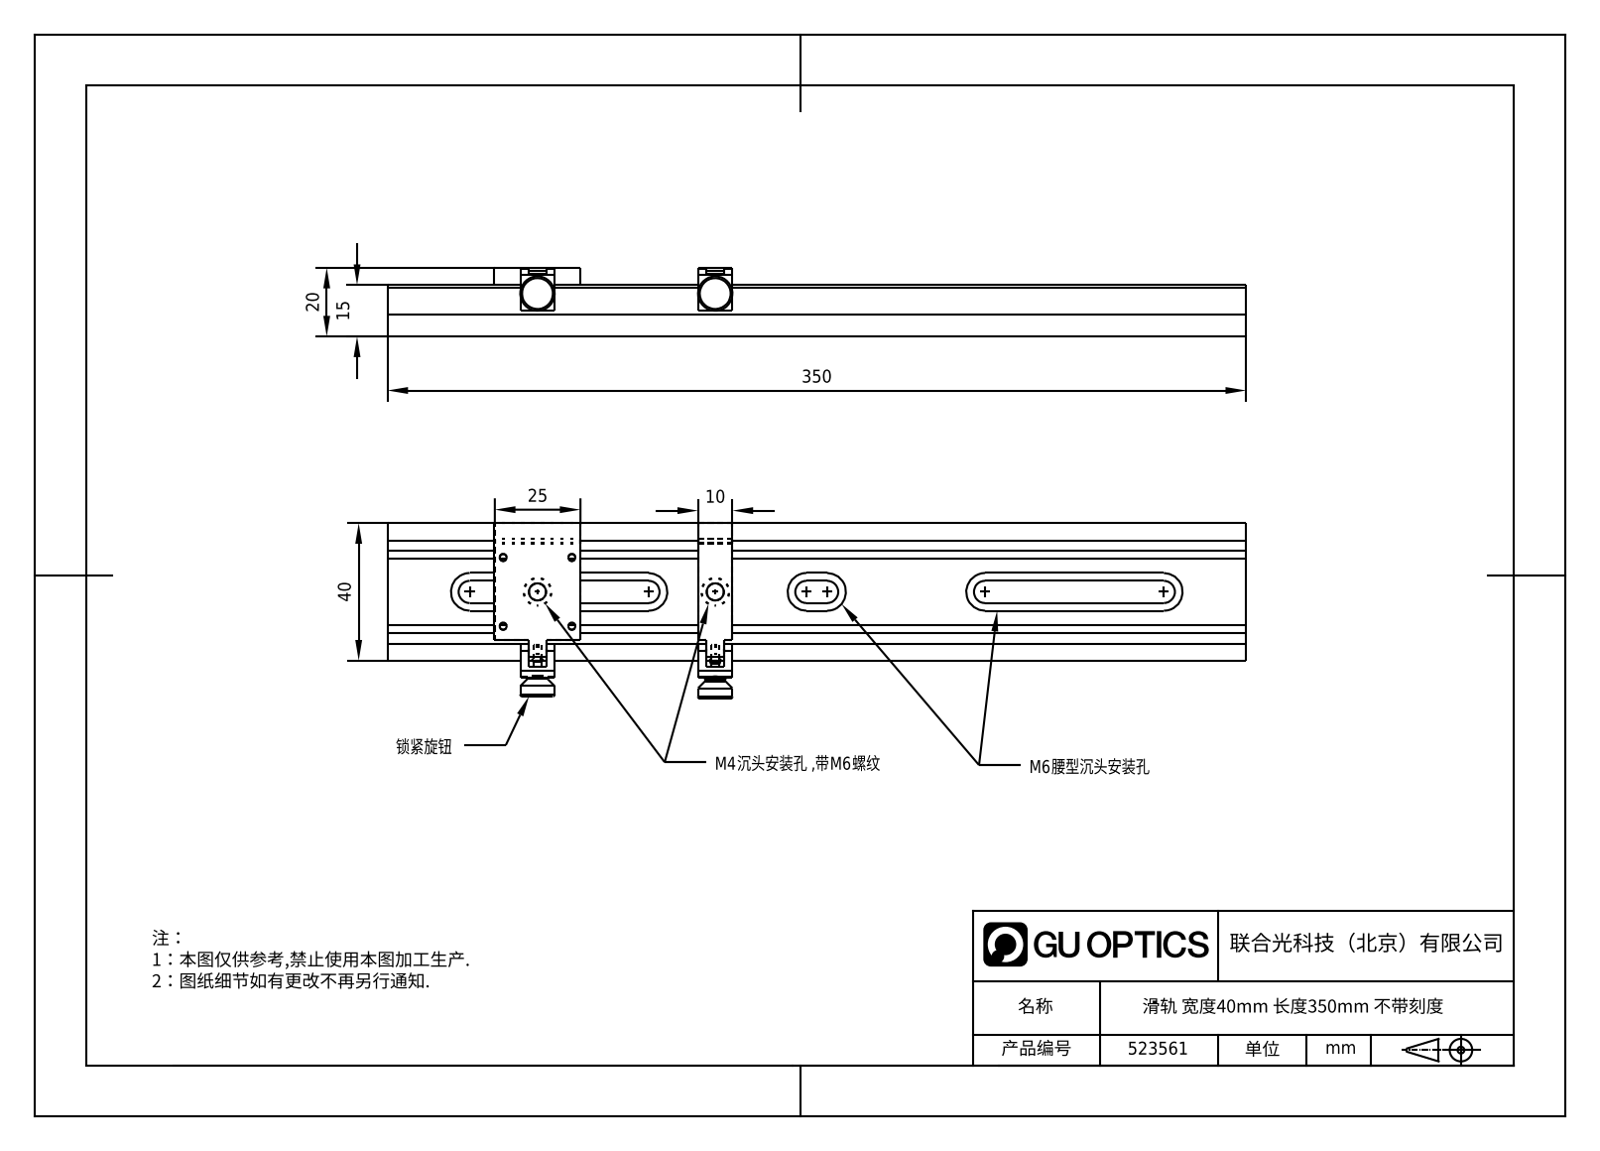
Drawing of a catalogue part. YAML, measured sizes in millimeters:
part_name: "4.2.1.10_H40G-350_40mm滑轨，长度350mm，附带两个H40Z滑轨安装座"
step_written_by: "SolidWorks 2021 (CONFIG_CONTROL_DESIGN)"
units: millimeters
bodies: {solids: 8, faces: 221, planar: 110, cylindrical: 83, other: 28}
overall_size: [350, 51.03, 20]
volume: 137252
surface_area: 52905
round_holes:
  - {diameter: 2.05, count: 4}
  - {diameter: 2.5, count: 2}
  - {diameter: 3.2, count: 2}
  - {diameter: 5, count: 2}
  - {diameter: 8, count: 2}
  - {diameter: 1.5, count: 1}
  - {diameter: 2, count: 1}
round_bosses_or_shafts:
  - {diameter: 10, count: 2}
  - {diameter: 6, count: 2}
  - {diameter: 3, count: 2}
  - {diameter: 2.2, count: 2}
partial_cylinders:
  - {radius: 3.25, count: 6}
  - {radius: 5.5, count: 6}
  - {radius: 1.25, count: 1}
  - {radius: 2.5, count: 1}
  - {radius: 4.5, count: 1}
  - {radius: 12.5, count: 1}
face_to_face_distances: [6, 14.5, 0.5, 6.5, 15, 8.5, 5, 40, 8, 14]
hole_center_spacings: [14.14, 20, 28.28, 67.16, 76.41, 86.99]
